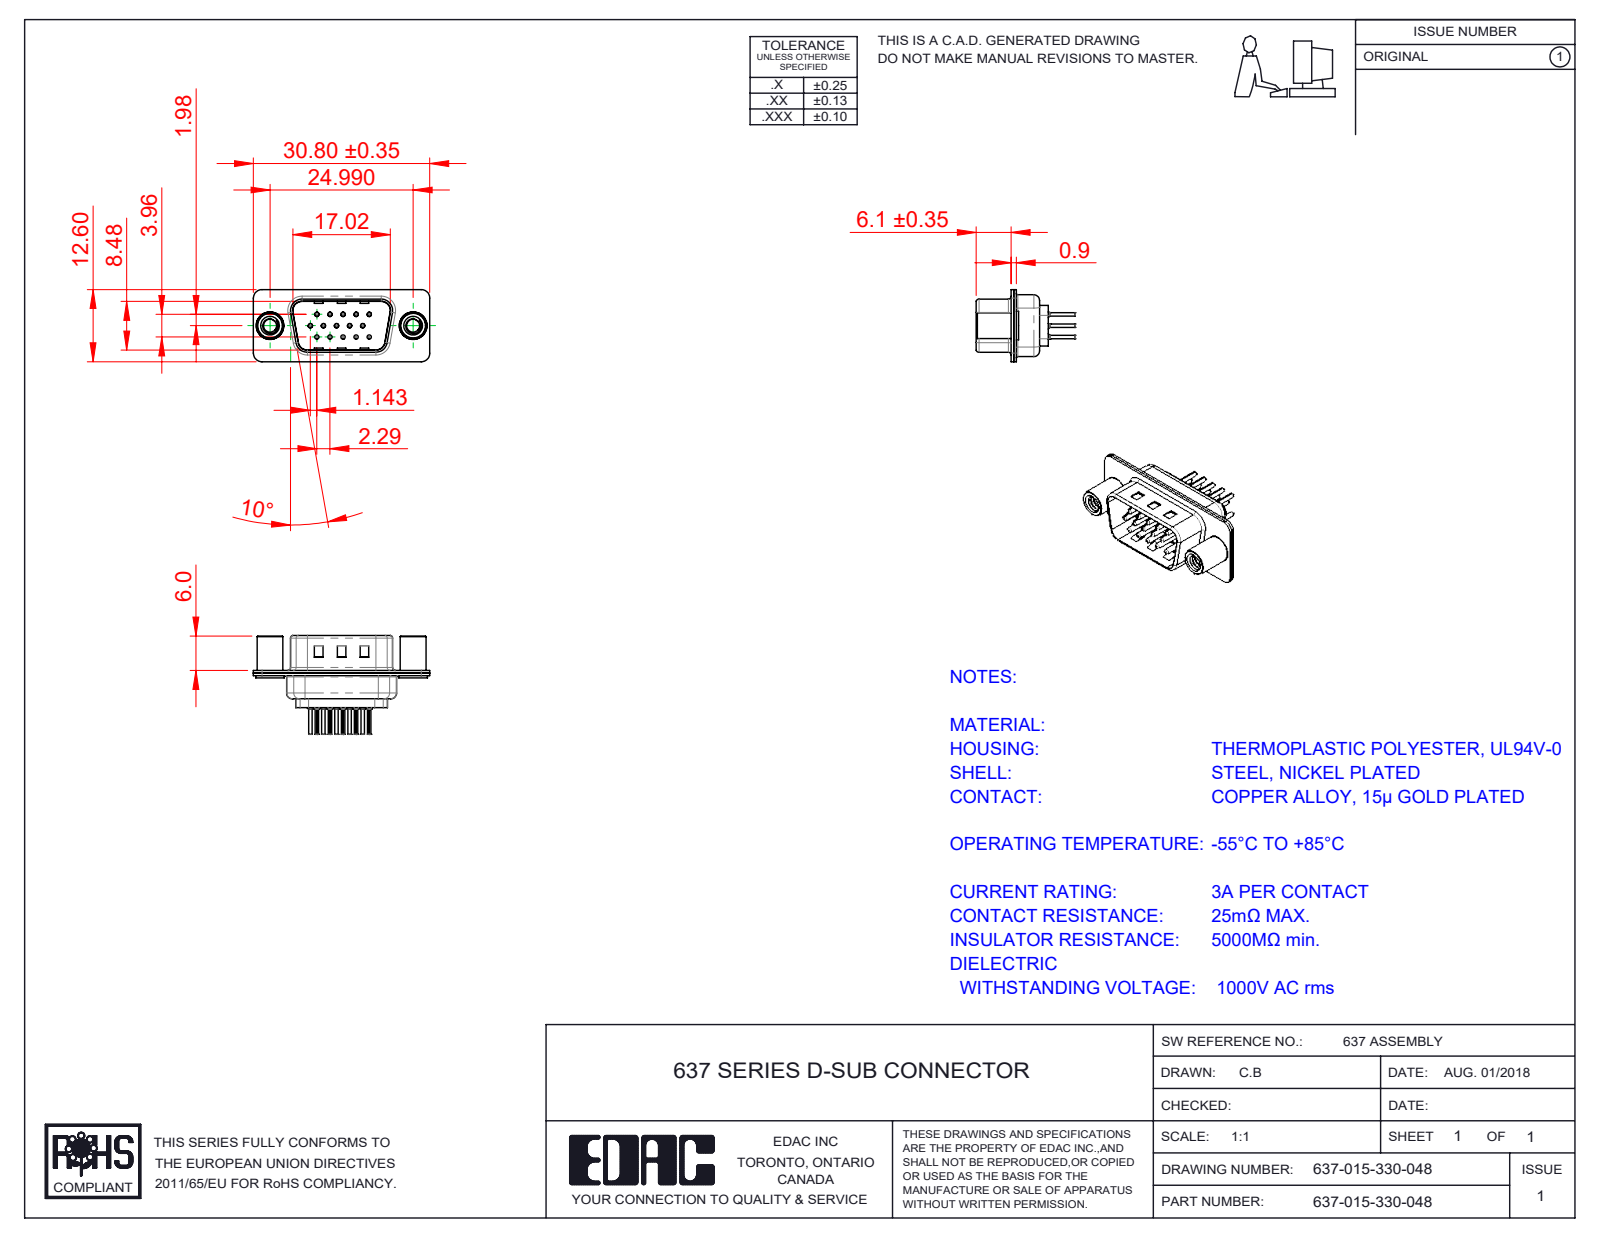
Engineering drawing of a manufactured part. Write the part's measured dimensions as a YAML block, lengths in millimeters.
part_name: "637-015-330-068; 637 Contact Row 3_30; 637 Housing_15 Contacts; 637 Shell Front_15 Contacts (+4 more)"
step_written_by: "SolidWorks 2020 (CONFIG_CONTROL_DESIGN)"
units: millimeters
bodies: {solids: 20, faces: 1838, planar: 469, cylindrical: 712, other: 657}
overall_size: [30.8, 17.25, 12.6]
volume: 1379
surface_area: 4840
round_holes:
  - {diameter: 0.2, count: 15}
  - {diameter: 0.35, count: 15}
  - {diameter: 1.1, count: 15}
  - {diameter: 1.6, count: 15}
  - {diameter: 2.26, count: 2}
  - {diameter: 4, count: 2}
  - {diameter: 4.8, count: 2}
round_bosses_or_shafts:
  - {diameter: 2, count: 15}
  - {diameter: 1.5, count: 15}
  - {diameter: 0.75, count: 15}
  - {diameter: 0.6, count: 15}
  - {diameter: 5, count: 2}
  - {diameter: 4.9, count: 2}
  - {diameter: 4.5, count: 2}
partial_cylinders:
  - {radius: 0.1, count: 30}
  - {radius: 1.5, count: 16}
  - {radius: 2, count: 12}
  - {radius: 0.5, count: 8}
  - {radius: 0.25, count: 4}
  - {radius: 0.55, count: 4}
  - {radius: 0.7, count: 4}
  - {radius: 0.95, count: 4}
face_to_face_distances: [0.45, 0.9, 0.4, 0.7, 8.88, 8.48, 1.05, 0.31, 4.55, 1.16]
hole_center_spacings: [3.96, 2.28, 4.57, 2.29, 6.05, 6.86, 7.92, 6.04]
